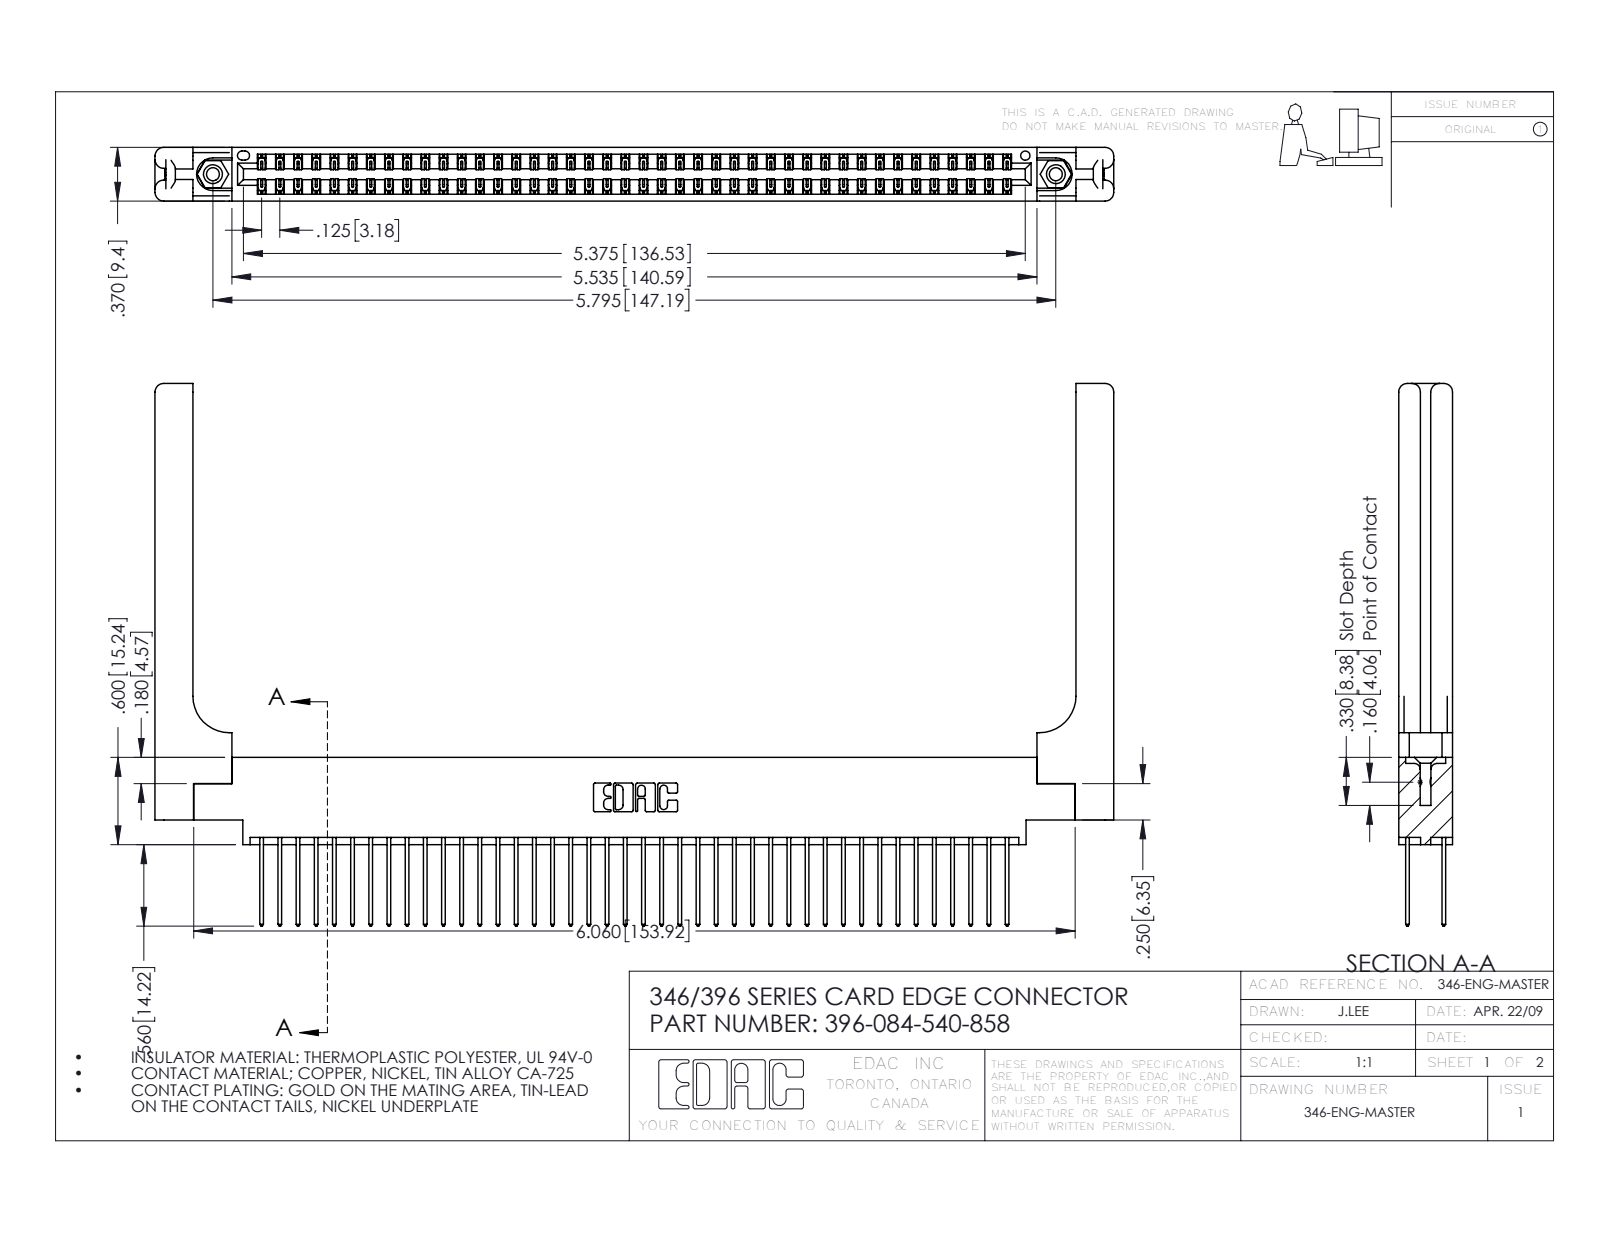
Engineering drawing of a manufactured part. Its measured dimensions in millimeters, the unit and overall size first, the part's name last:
Units: millimetres
Overall size (bounding box): 167.4 × 94.7 × 9.4
Round holes (diameter × count): ⌀2.3 ×2, ⌀3.2 ×2, ⌀4 ×2, ⌀1.6 ×1
Round bosses / shafts (diameter × count): ⌀3.9 ×2
Partial cylindrical surfaces — rounded edges, fillets, slot ends (radius × count): R0.2 ×126, R0.3 ×84, R0.3 ×22, R1.5 ×16, R0.2 ×6, R0.8 ×6, R0.7 ×3, R0.4 ×2
Main face-to-face distances: 1.2, 8.2, 9.4, 1.8, 6.4, 0.6, 7.6, 3.8, 3.8, 7
Hole centre spacings: 6.2, 141.9, 147.2
Volume: 23 990 mm³ · Surface area: 29 320 mm²
Bodies: 89 solids, 4750 faces (3168 planar, 1522 cylindrical, 60 other)
Part name (STEP PRODUCT): 345-250-001_345-250-001-102; 396-084-540-858; 345-292-001_345-293-140; 346 Part_0.170 Offset - 0.156 Dia-TH (+1 more)
STEP written by: SolidWorks 2016 (CONFIG_CONTROL_DESIGN)
